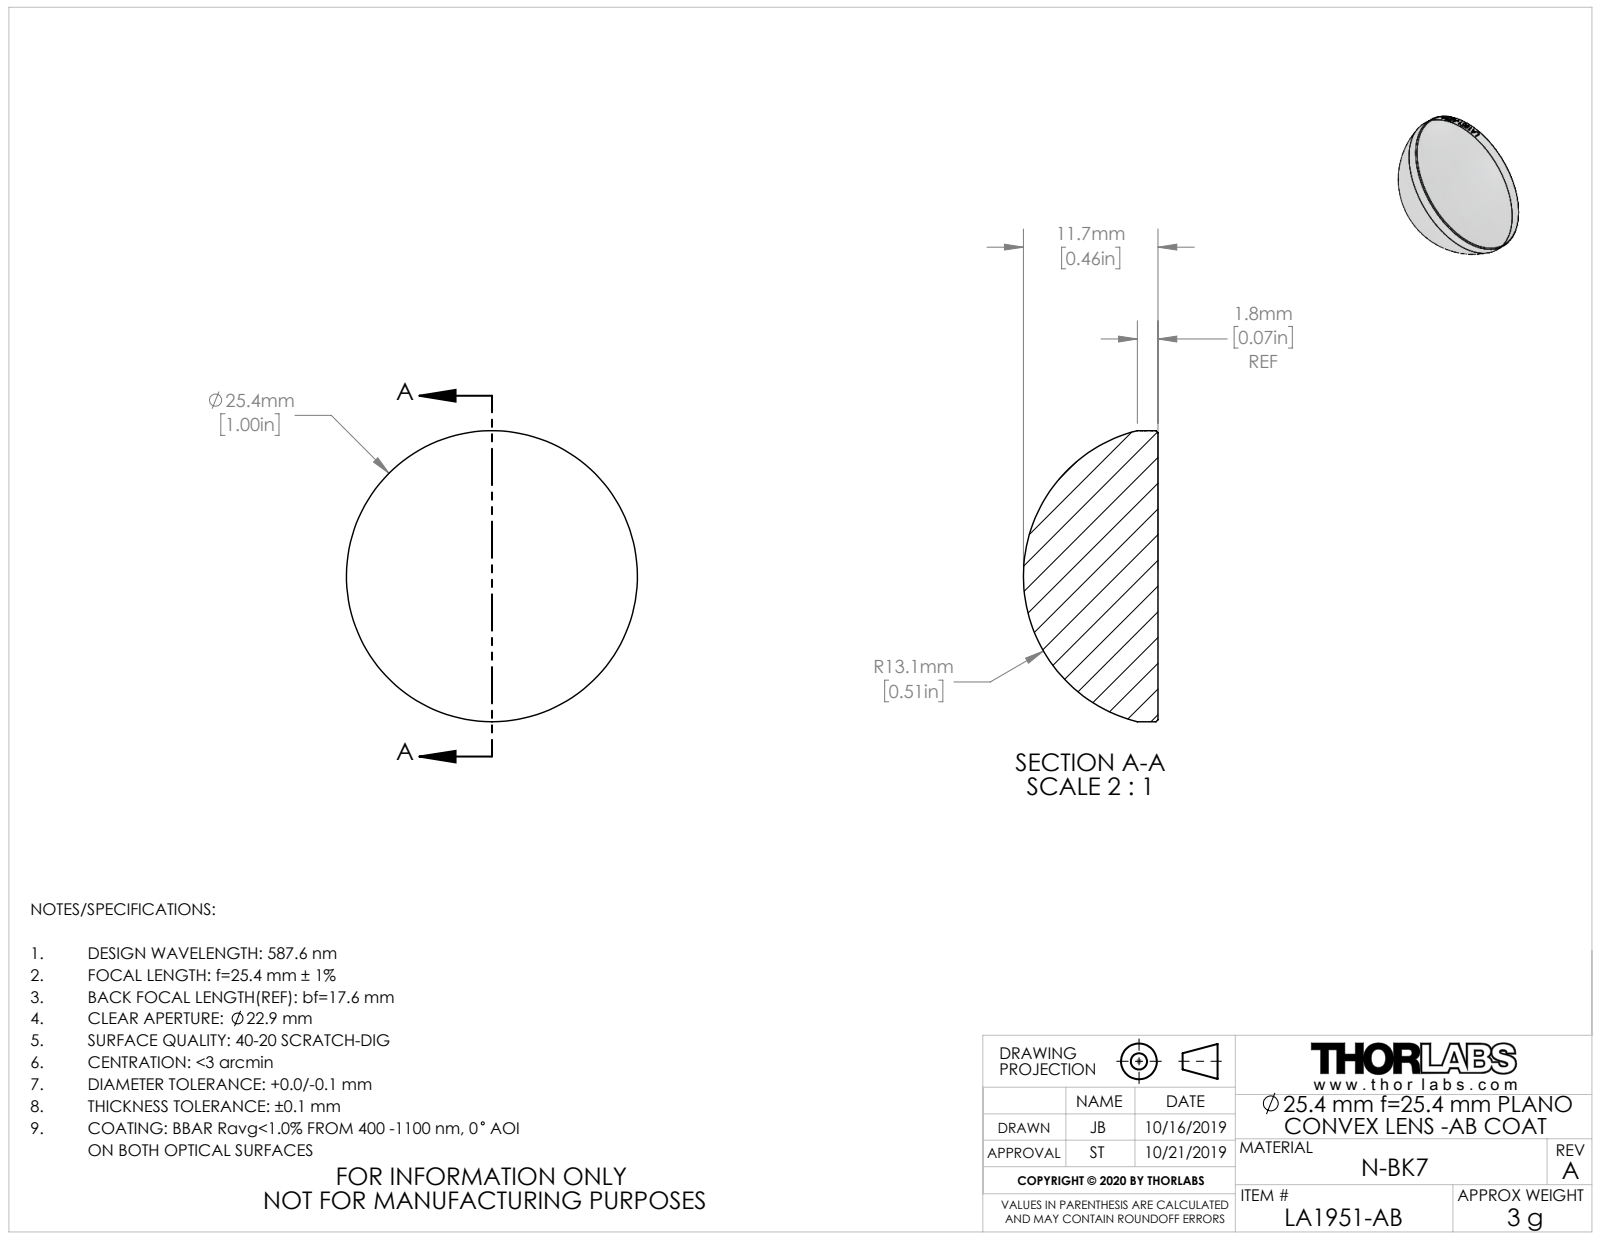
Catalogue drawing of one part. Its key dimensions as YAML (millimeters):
part_name: "TTN195777-E0W"
step_written_by: "SolidWorks 2018 (CONFIG_CONTROL_DESIGN)"
units: millimeters
bodies: {solids: 1, faces: 27, planar: 1, cylindrical: 22, other: 4}
overall_size: [25.4, 25.4, 11.7]
volume: 3950
surface_area: 1459
round_bosses_or_shafts:
  - {diameter: 25.4, count: 1}
